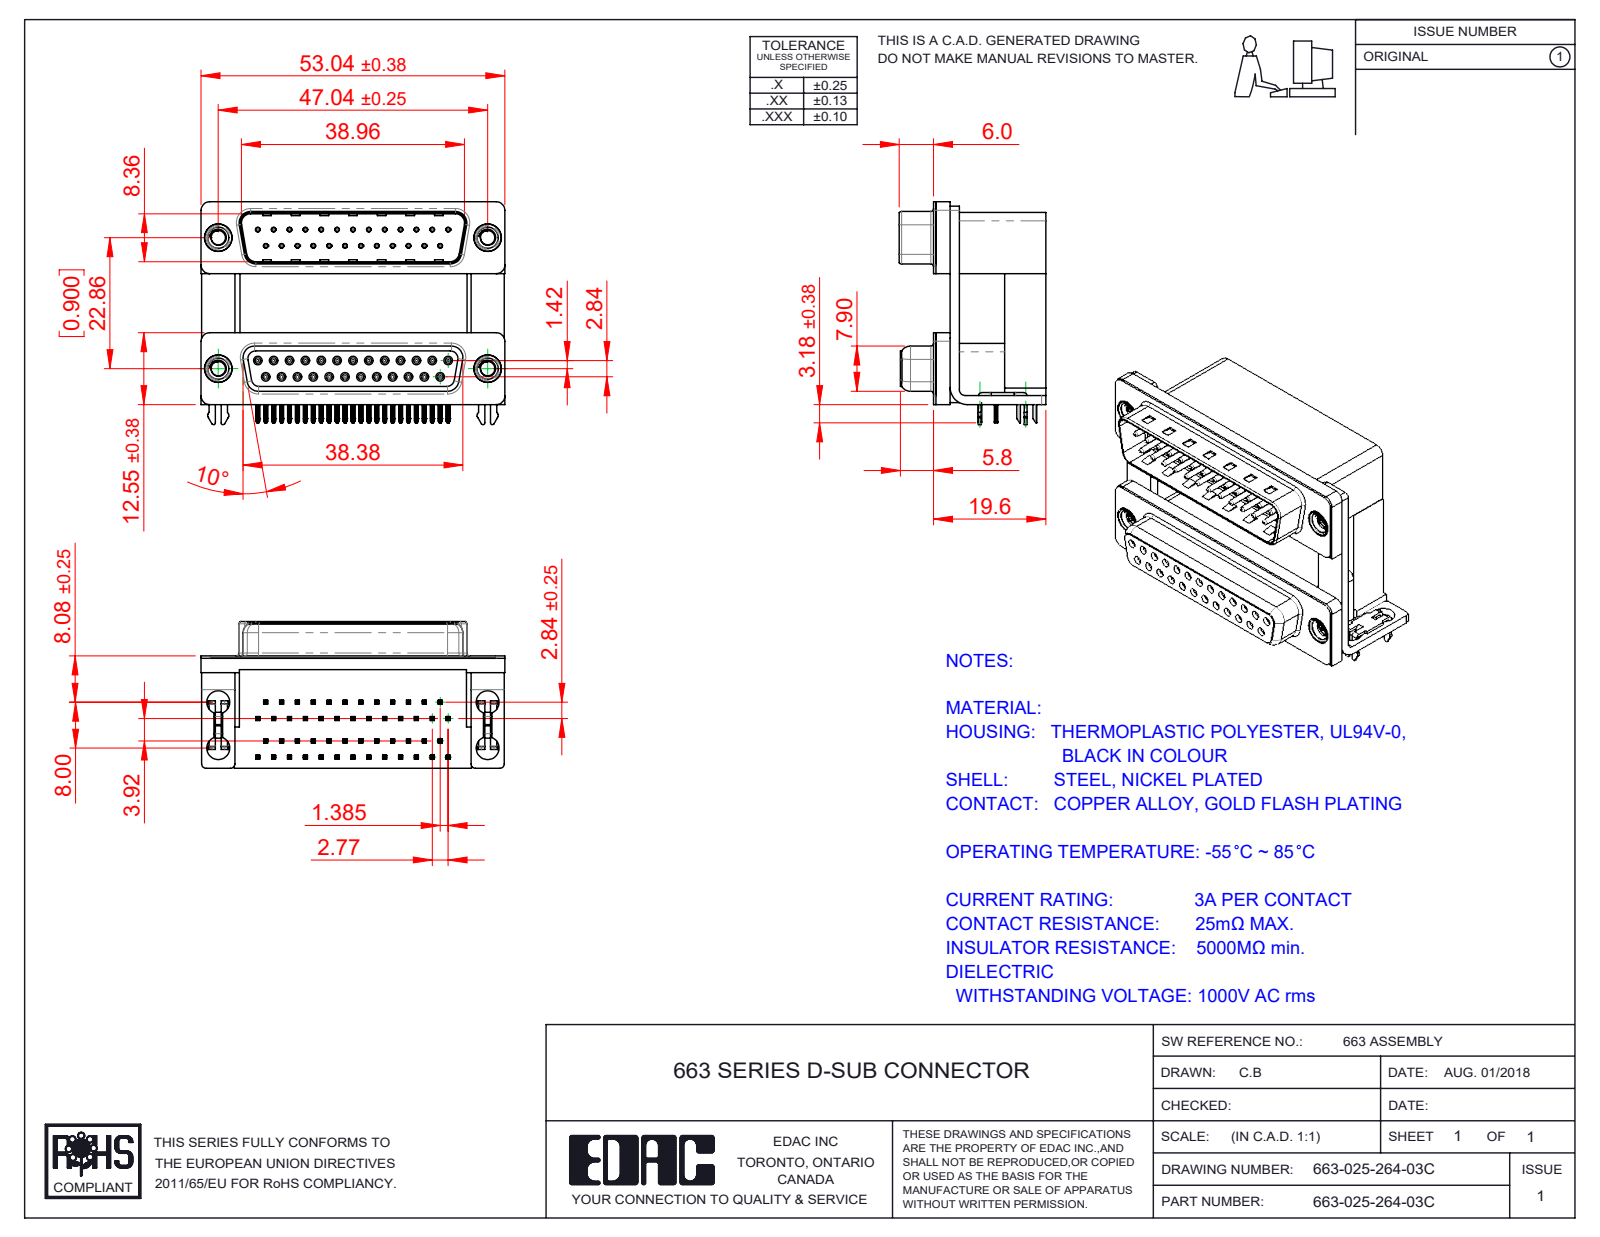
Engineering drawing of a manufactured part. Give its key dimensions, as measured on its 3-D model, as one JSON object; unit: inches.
{"part_name": "663 Threaded Rivet_M3; 663-025-264-03C; 663 Mounting Bracket_2ProngH; 663 Housing Upper_25 Contacts H (+8 more)", "step_written_by": "SolidWorks 2020 (CONFIG_CONTROL_DESIGN)", "units": "inches", "bodies": {"solids": 63, "faces": 6359, "planar": 3359, "cylindrical": 1601, "other": 1399}, "overall_size": [2.088, 1.532, 1.008], "volume_in3": 1.447, "surface_area_in2": 39.04, "round_holes": [[0.031, 50], [0.014, 25], [0.035, 25], [0.157, 8], [0.098, 4], [0.138, 4], [0.189, 4], [0.197, 4]], "round_bosses_or_shafts": [[0.047, 25], [0.03, 25], [0.193, 4], [0.187, 4], [0.154, 4]], "partial_cylinders_radius": [[0.004, 202], [0.01, 110], [0.006, 100], [0.005, 50], [0.014, 50], [0.013, 25], [0.02, 16], [0.059, 14]], "face_to_face_distances": [0.756, 0.472, 0.283, 0.016, 0.421, 0.657, 0.374, 0.098, 0.9, 0.488], "hole_center_spacings": [0.124, 0.109, 0.218, 0.436, 0.327, 0.198, 0.545, 0.294]}
